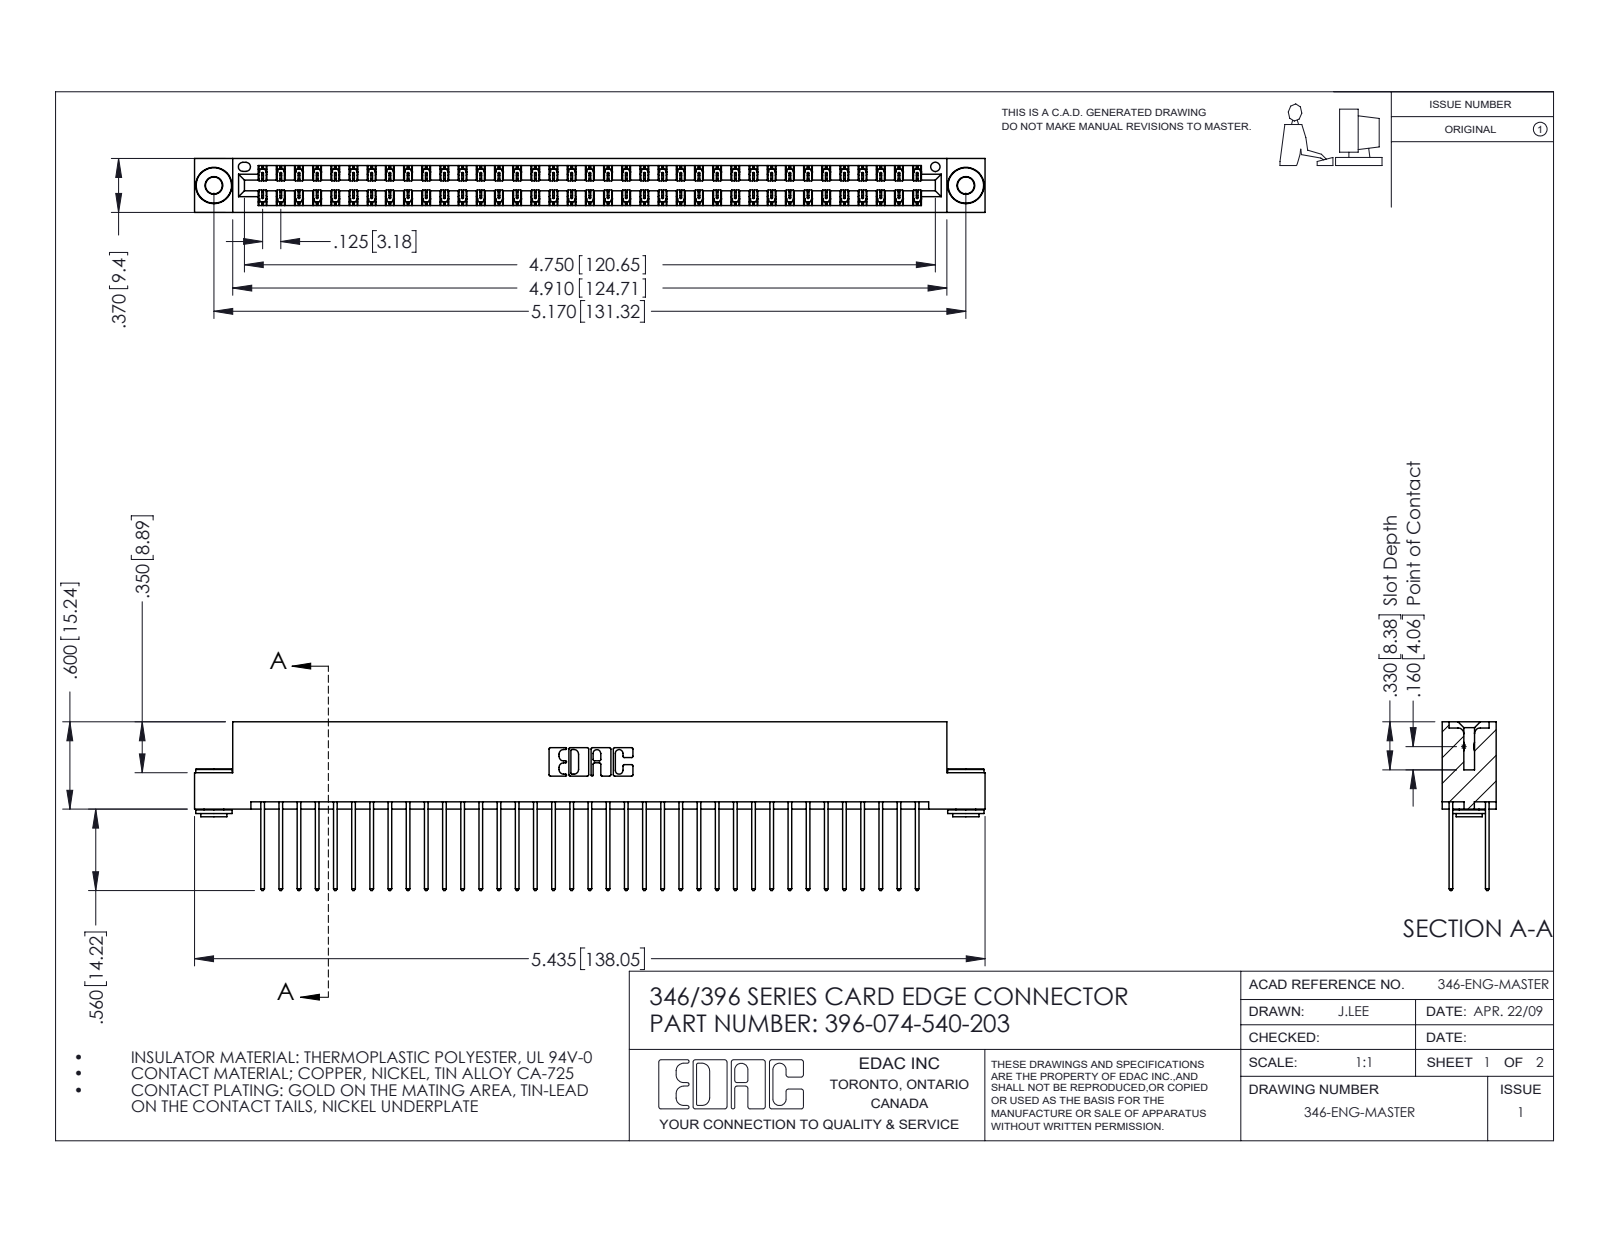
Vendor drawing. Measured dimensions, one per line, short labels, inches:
name: 396-074-540-203; 345-250-002_345-250-002-102; 345-292-001_345-293-140; 346 Part_Flush Mounting Lugs - 0.156 Dia-TH
written by: SolidWorks 2016 (CONFIG_CONTROL_DESIGN)
unit: in
bodies: 77 solids, 4008 faces (2676 planar, 1324 cylindrical, 8 other)
size: 5.435 × 1.16 × 0.37
volume: 0.837 in³; area: 31.5 in²
holes: 2× ⌀0.116, 2× ⌀0.156, 1× ⌀0.064
bosses: 2× ⌀0.25, 2× ⌀0.18, 2× ⌀0.136
rounds: 111× R0.006, 74× R0.01, 22× R0.01, 6× R0.007, 6× R0.031, 3× R0.026, 2× R0.014, 2× R0.022
face distances: 0.048, 0.322, 0.25, 0.025, 0.072, 0.298, 0.37, 0.275, 0.148, 0.222
hole spacings: 0.246, 4.961, 5.17
